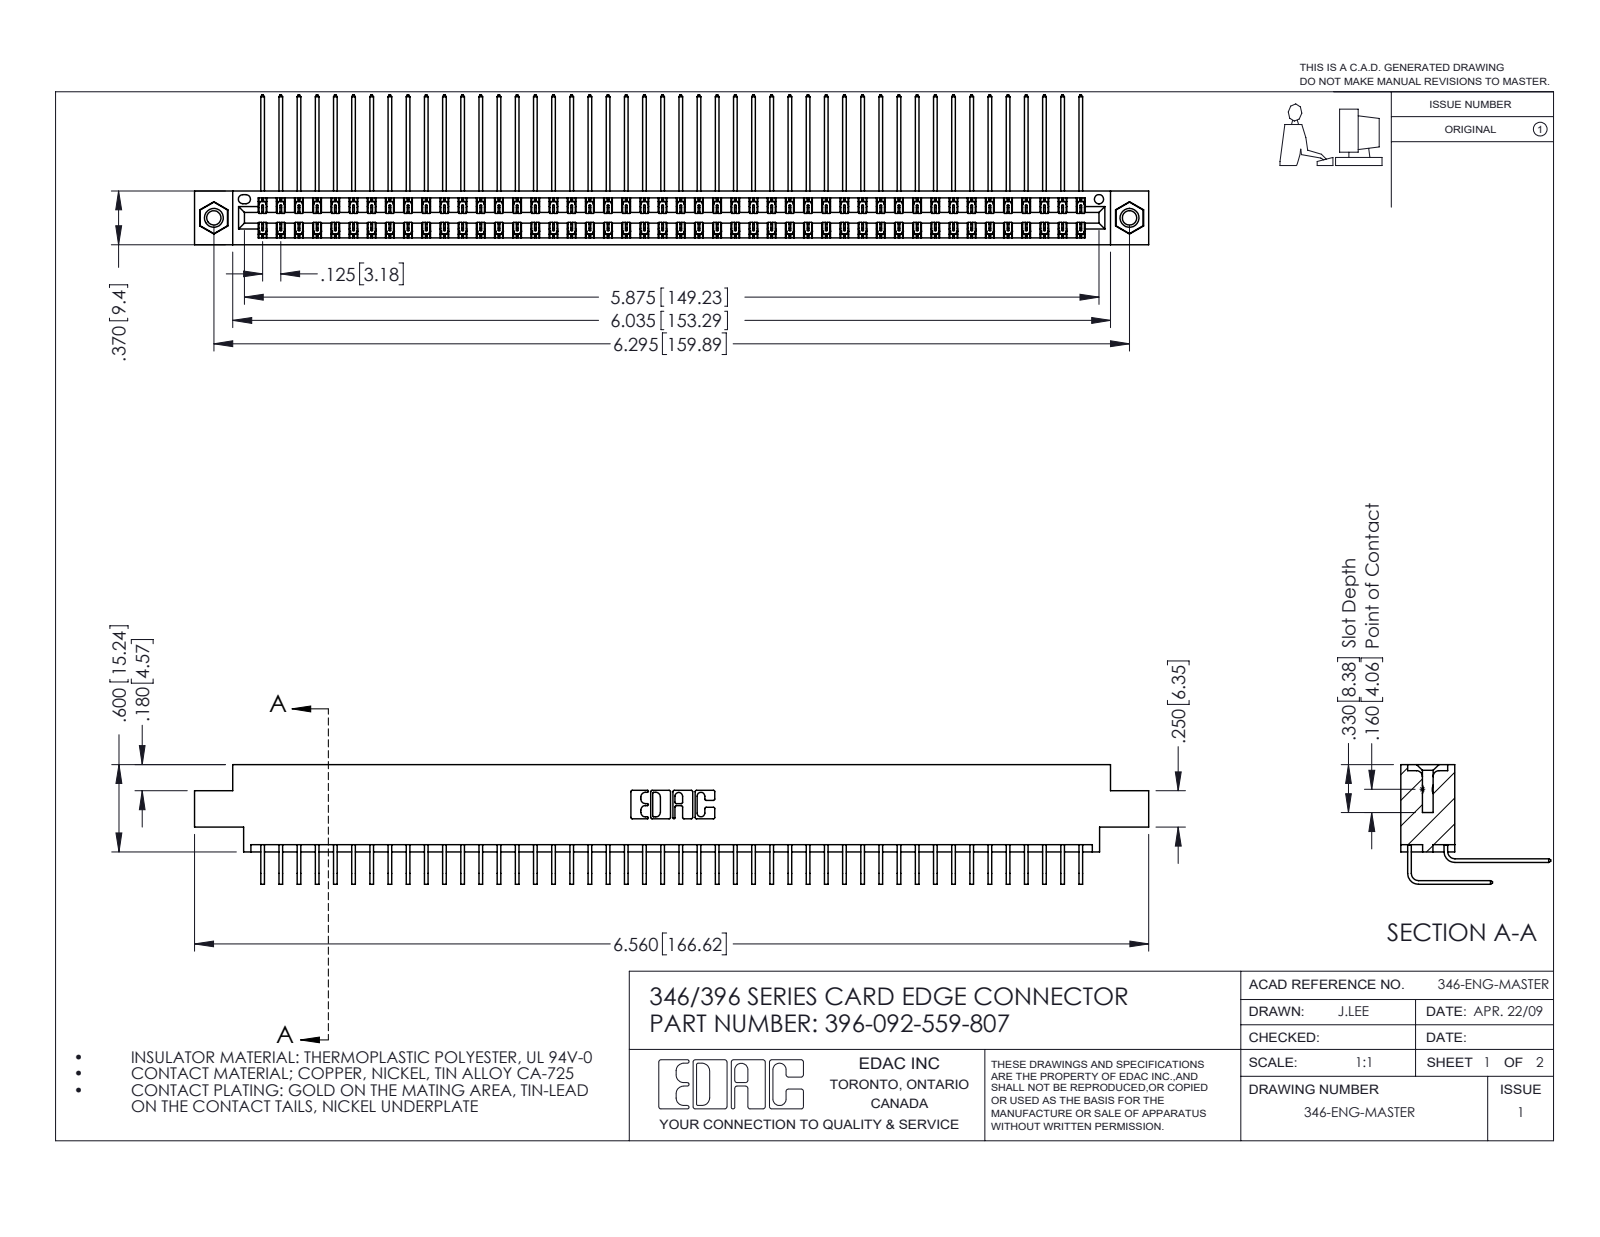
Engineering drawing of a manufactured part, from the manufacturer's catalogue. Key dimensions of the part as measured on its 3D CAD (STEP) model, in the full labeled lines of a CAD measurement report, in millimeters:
Part name (STEP PRODUCT): 345-292-001_559 Tail - 2; 345-292-001_558 559 Tail - 1; 346 Part_0.170 Offset - 0.156 Dia-TI; 396-092-559-807 (+1 more)
STEP written by: SolidWorks 2016 (CONFIG_CONTROL_DESIGN)
Units: millimetres
Bodies: 95 solids, 5154 faces (3516 planar, 1622 cylindrical, 16 other)
Overall size (bounding box): 166.6 × 26.2 × 20.9
Volume: 16 650 mm³ · Surface area: 25 700 mm²
Round holes (diameter × count): ⌀2.5 ×2, ⌀3.2 ×2, ⌀4 ×2, ⌀1.6 ×1
Round bosses / shafts (diameter × count): ⌀3.9 ×2
Partial cylindrical surfaces — rounded edges, fillets, slot ends (radius × count): R0.2 ×138, R0.3 ×22, R0.2 ×6, R0.8 ×6, R0.7 ×3, R0.4 ×2, R0.6 ×2, R0.6 ×2
Main face-to-face distances: 1.2, 8.2, 0.6, 9.4, 6.4, 1.8, 7.6, 7, 5.6, 3.8
Hole centre spacings: 6.2, 154.6, 159.9
